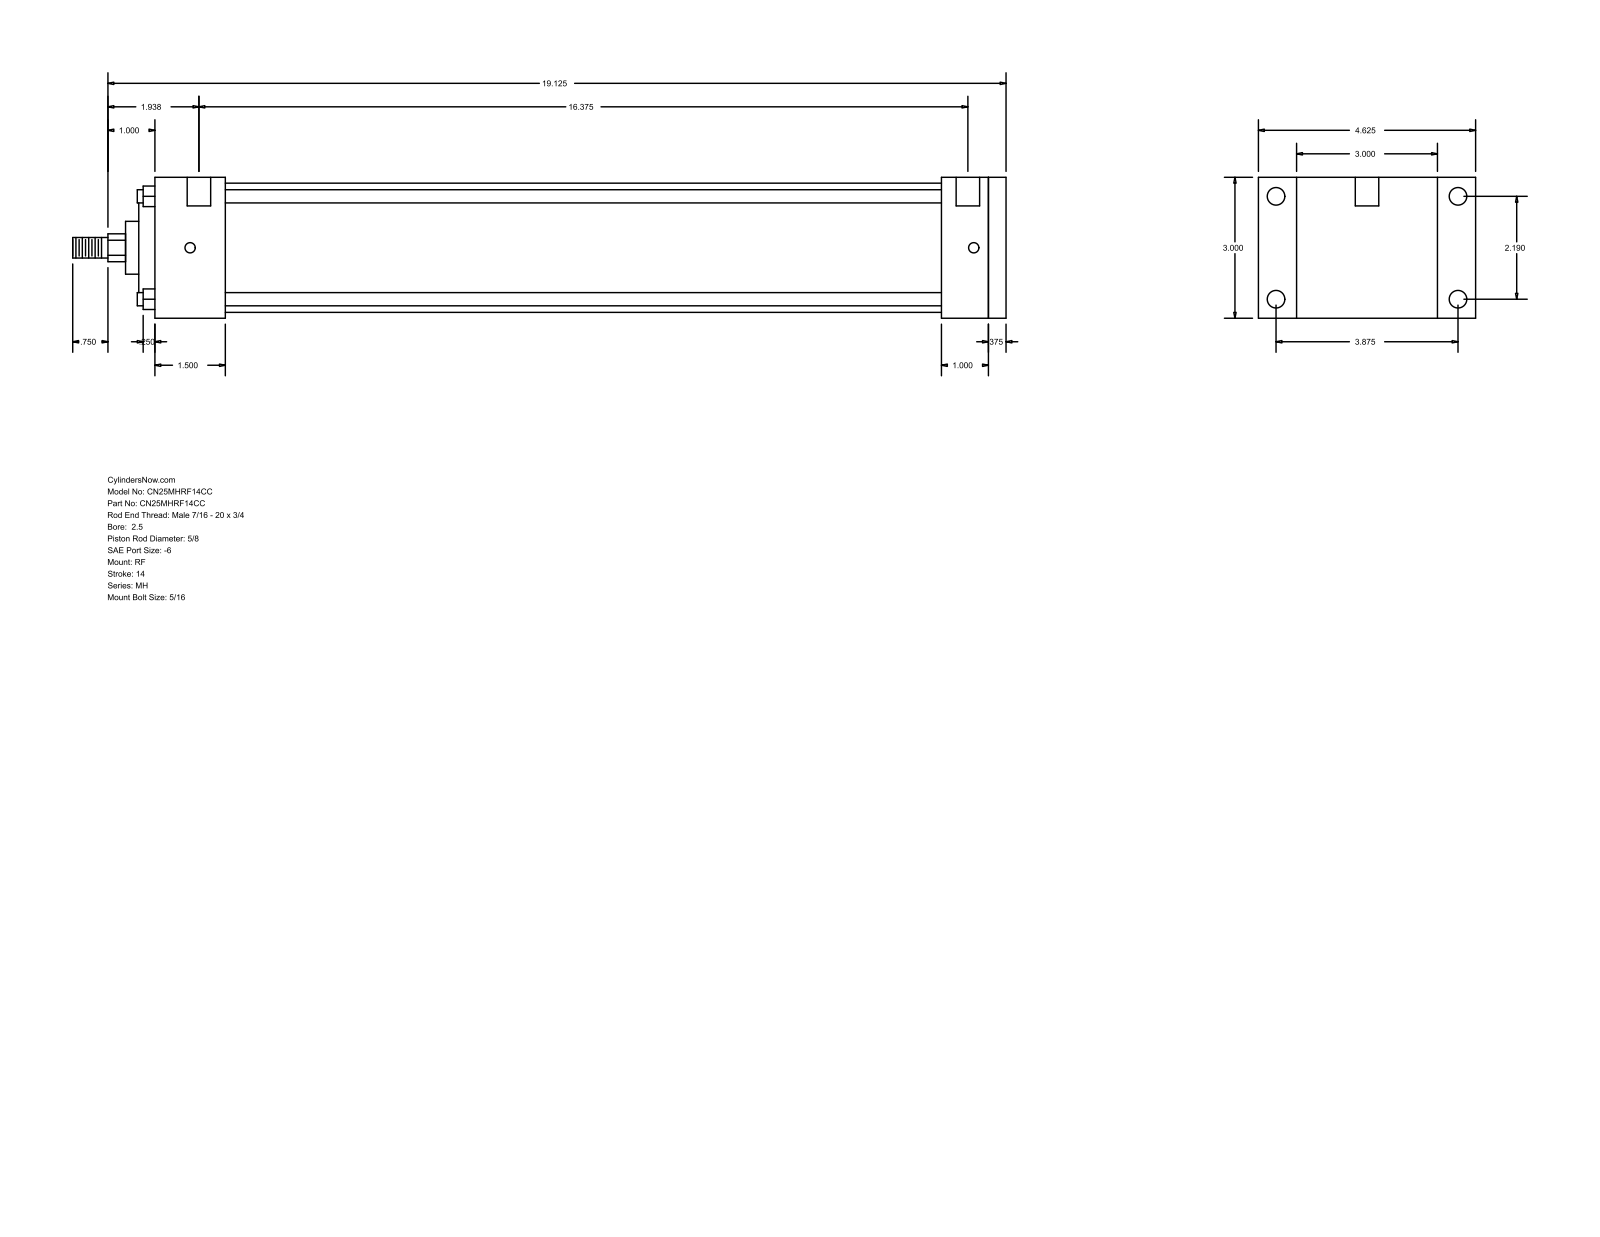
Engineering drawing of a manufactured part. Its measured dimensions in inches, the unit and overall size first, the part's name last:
Units: inches
Overall size (bounding box): 19.875 × 4.625 × 3
Round holes (diameter × count): ⌀0.219 ×4, ⌀0.375 ×4, ⌀0.5 ×2
Round bosses / shafts (diameter × count): ⌀0.281 ×4, ⌀2.75 ×1, ⌀2.187 ×1, ⌀1.125 ×1, ⌀0.625 ×1, ⌀0.437 ×1
Partial cylindrical surfaces — rounded edges, fillets, slot ends (radius × count): R0.297 ×1
Main face-to-face distances: 3, 0.375, 18.125, 17.75, 1, 1.5, 16.75, 1.375, 15.25, 16.25
Hole centre spacings: 2.19, 3.875, 4.451, 16.687, 0.125, 0.187, 16.375, 16.5
Bodies: 0 solids, 94 faces (65 planar, 29 cylindrical, 0 other)
Part name (STEP PRODUCT): MH_RF__0250_0.625
STEP written by: GSSL Pune (CONFIG_CONTROL_DESIGN)
